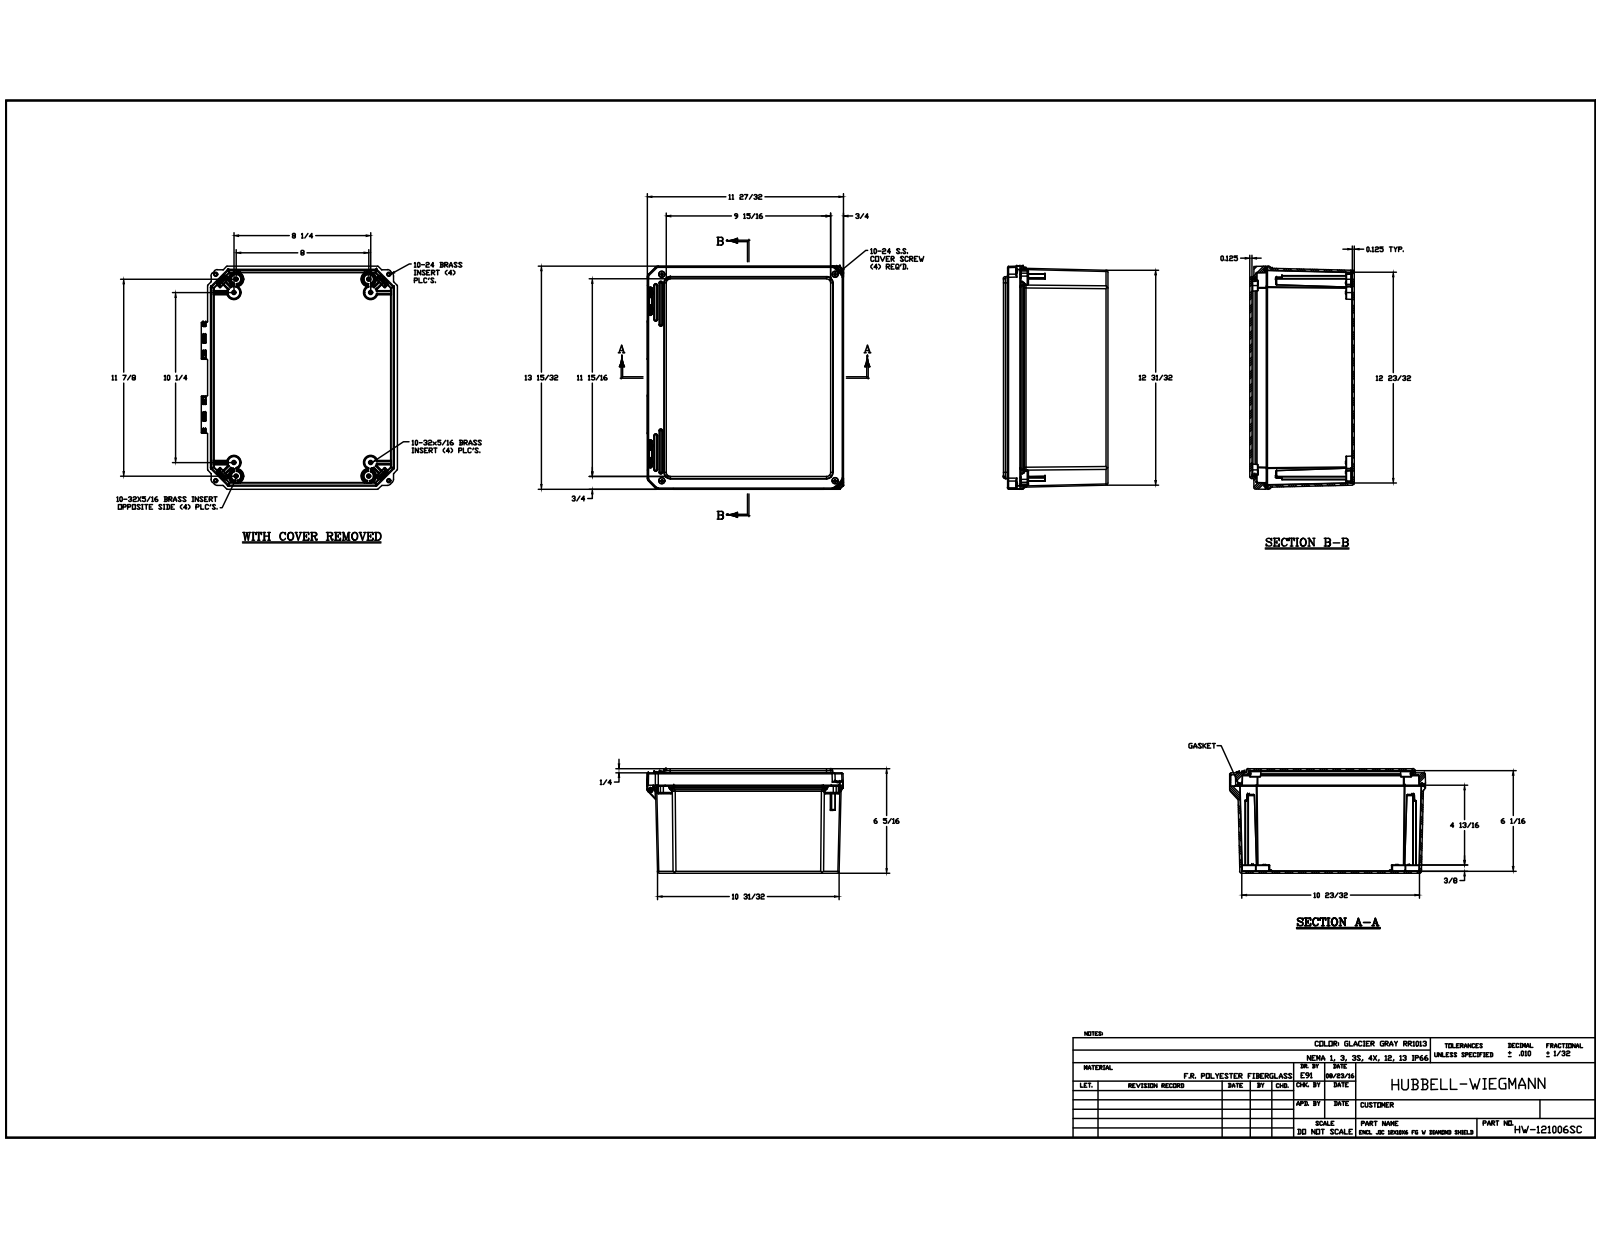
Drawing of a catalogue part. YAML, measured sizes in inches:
part_name: "HW-121006SC; DS121006BOX; BRASS INSERT-(; BRASS INSERT-(_1 (+6 more)"
step_written_by: "Autodesk Inventor 2017 (CONFIG_CONTROL_DESIGN)"
units: inches
bodies: {solids: 27, faces: 2079, planar: 683, cylindrical: 758, other: 638}
overall_size: [13.46, 11.831, 6.31]
volume: 93.12
surface_area: 1269
round_holes:
  - {diameter: 0.156, count: 16}
  - {diameter: 0.152, count: 8}
  - {diameter: 0.252, count: 4}
  - {diameter: 0.253, count: 4}
  - {diameter: 0.219, count: 2}
  - {diameter: 0.227, count: 2}
  - {diameter: 0.313, count: 2}
  - {diameter: 0.137, count: 1}
round_bosses_or_shafts:
  - {diameter: 0.246, count: 16}
  - {diameter: 0.87, count: 4}
  - {diameter: 0.45, count: 4}
  - {diameter: 0.199, count: 4}
  - {diameter: 0.435, count: 2}
partial_cylinders:
  - {radius: 0.01, count: 157}
  - {radius: 0.005, count: 80}
  - {radius: 0.02, count: 57}
  - {radius: 0.03, count: 45}
  - {radius: 0.063, count: 26}
  - {radius: 0.03, count: 24}
  - {radius: 0.09, count: 24}
  - {radius: 0.096, count: 24}
face_to_face_distances: [0.125, 6.185, 6.31, 6.061, 0.139, 0.14, 0.14, 0.25, 5.935, 0.125]
hole_center_spacings: [0.824, 11.065, 11.406, 13.727, 9.417, 1.261, 1.559, 8.165]
